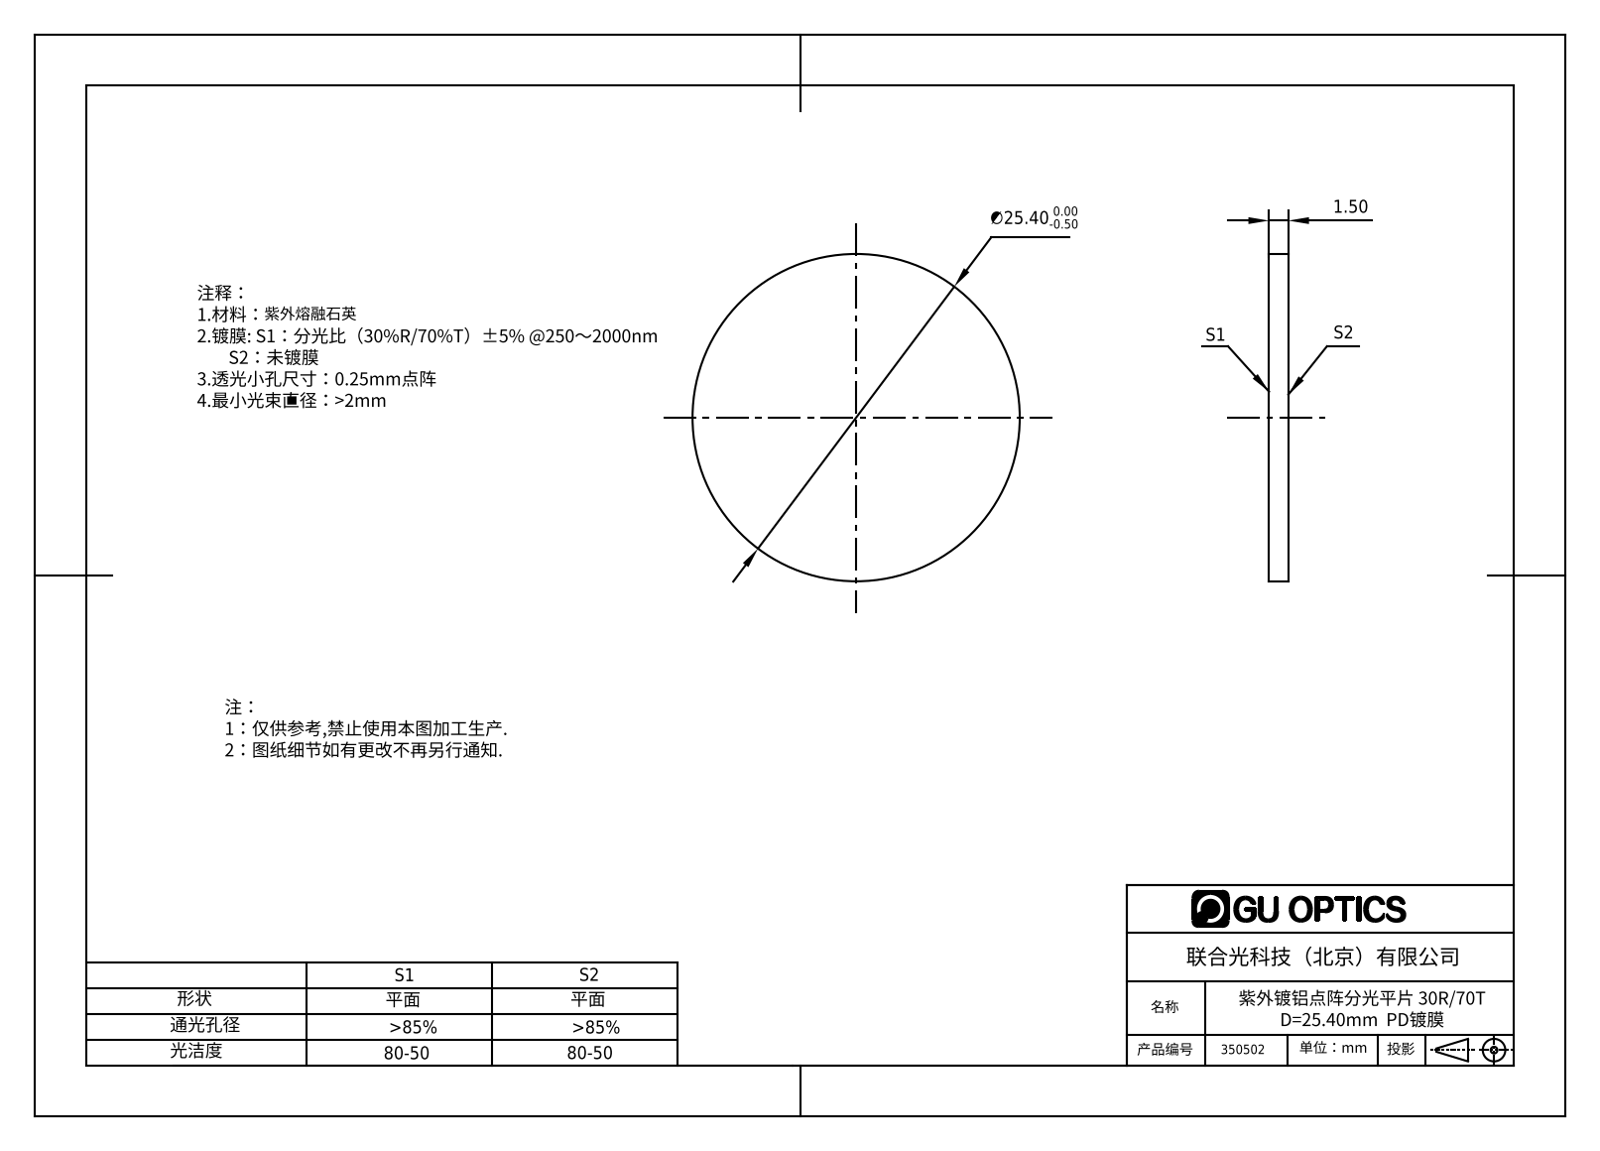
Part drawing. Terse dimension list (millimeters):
name: 350502
written by: SolidWorks 2016 (AUTOMOTIVE_DESIGN)
unit: mm
bodies: 1 solid, 4 faces (2 planar, 2 cylindrical, 0 other)
size: 25.4 × 25.4 × 1.5
volume: 760 mm³; area: 1 133 mm²
bosses: 1× ⌀25.4
face distances: 1.5
